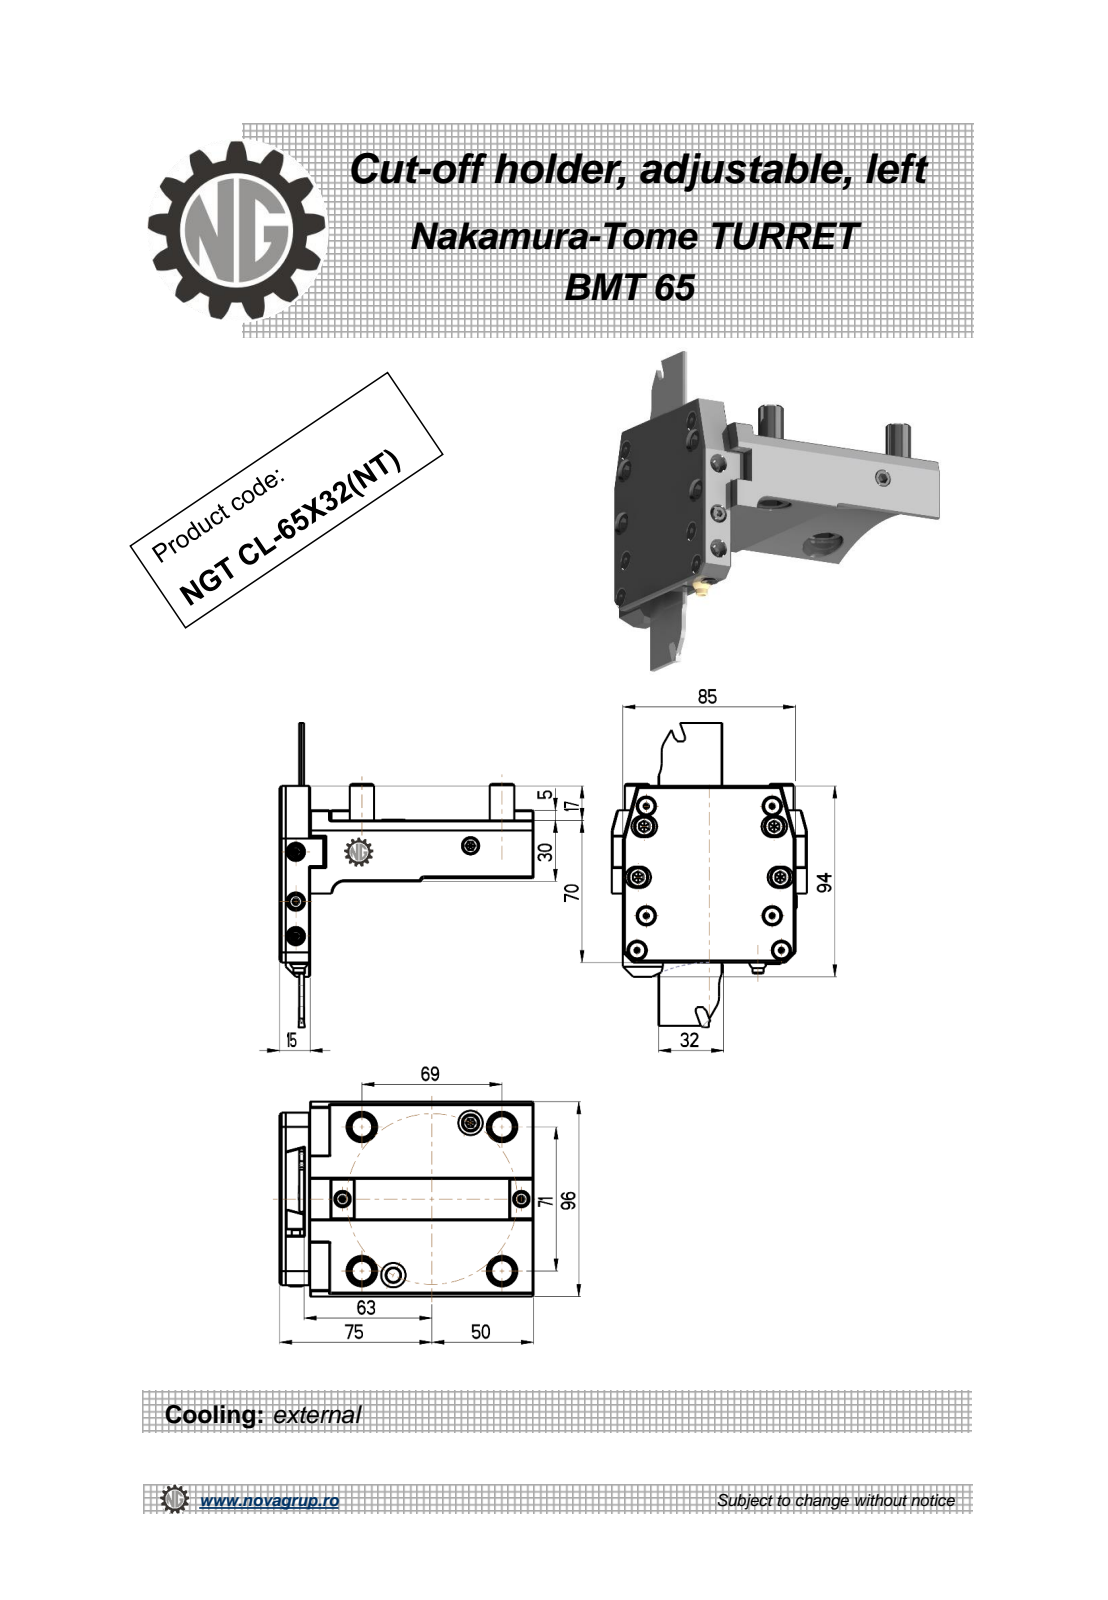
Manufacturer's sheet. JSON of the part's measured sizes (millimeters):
{"part_name": "NGT_CL_65_32_NT", "step_written_by": "PRO/ENGINEER BY PARAMETRIC TECHNOLOGY CORPORATION, 2010280 (CONFIG_CONTROL_DESIGN)", "units": "millimeters", "bodies": {"solids": 1, "faces": 487, "planar": 292, "cylindrical": 116, "other": 79}, "overall_size": [125, 96, 95], "volume_mm3": 352760, "surface_area_mm2": 68747, "round_holes": [[5, 2], [8, 2], [12, 2], [3.5, 1], [6.8, 1]], "round_bosses_or_shafts": [[12, 4], [10, 4], [4, 3], [8, 1], [7, 1], [5.5, 1]], "partial_cylinders_radius": [[0.2, 24], [0.31, 12], [5.25, 8], [0.14, 6], [0.16, 6], [0.41, 6], [1, 1], [6, 1]], "face_to_face_distances": [12, 3, 15, 30, 9, 5, 25, 96, 22, 110], "hole_center_spacings": [41.5, 48.42, 84.08, 104.51]}
